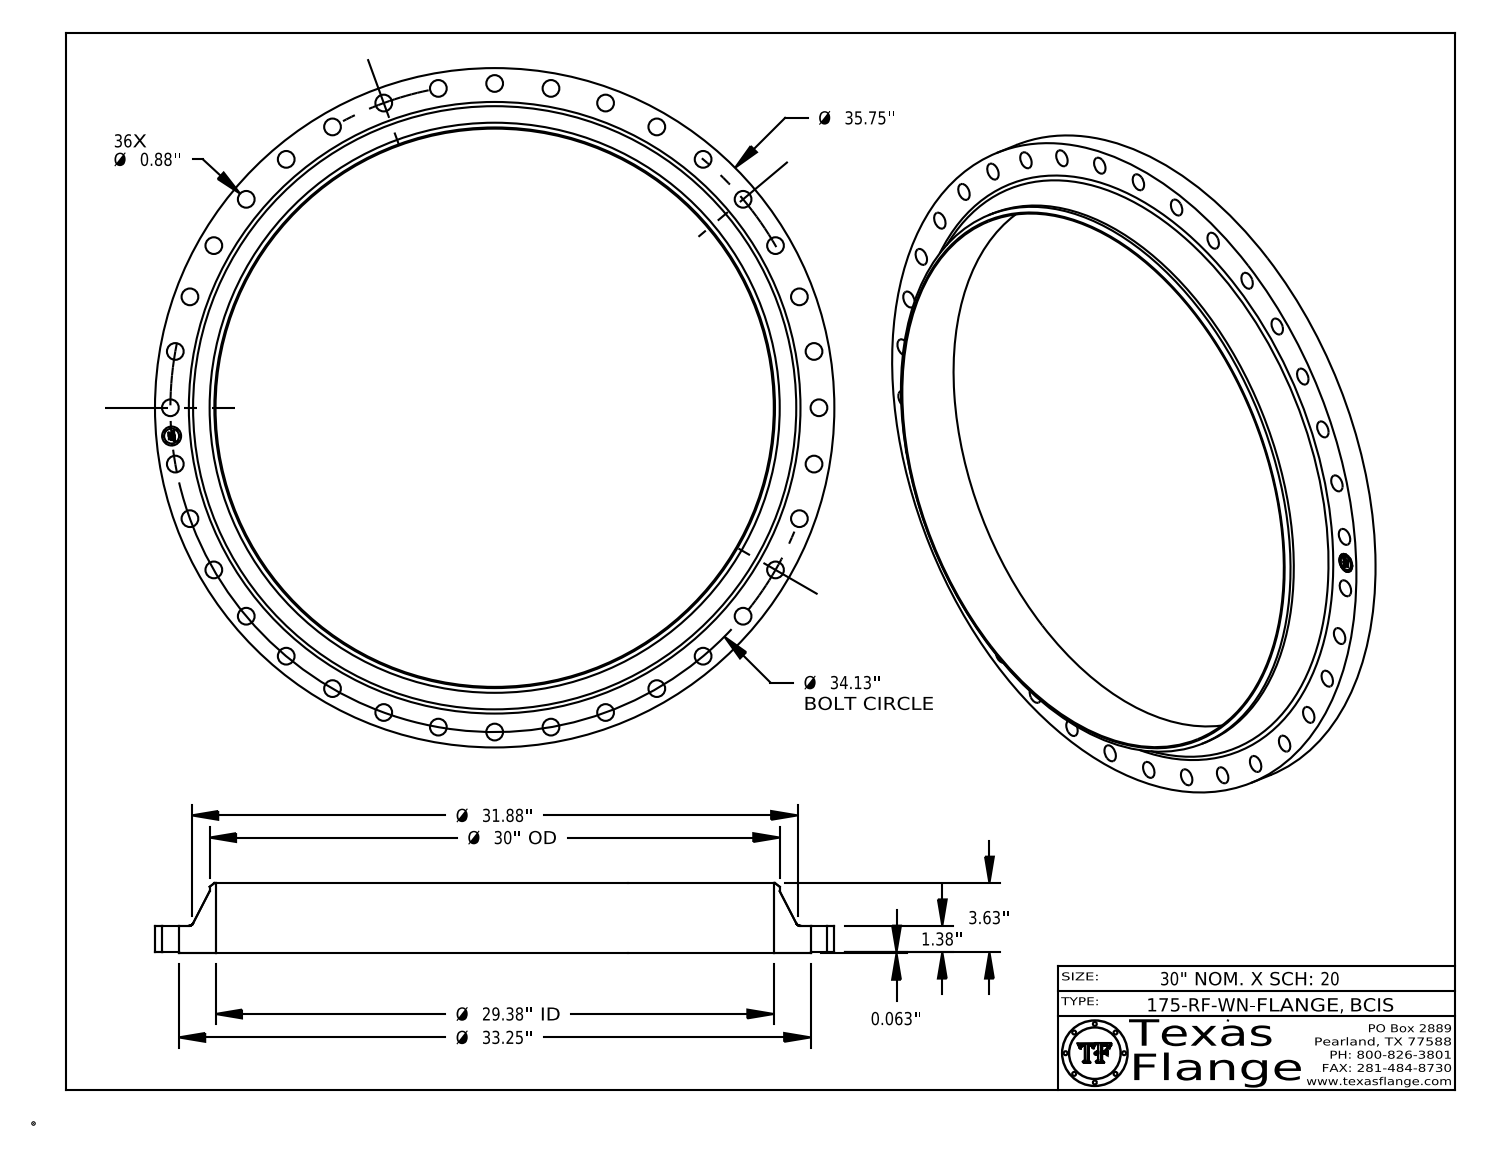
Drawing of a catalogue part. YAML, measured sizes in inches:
part_name: "175-RF-WN, BCIS"
step_written_by: "CATIA V5 STEP AP214 (AUTOMOTIVE_DESIGN)"
units: inches
bodies: {solids: 1, faces: 475, planar: 369, cylindrical: 100, other: 6}
overall_size: [35.75, 35.75, 3.693]
volume: 577.6
surface_area: 1381
round_holes:
  - {diameter: 0.88, count: 36}
  - {diameter: 1, count: 1}
  - {diameter: 29.376, count: 1}
round_bosses_or_shafts:
  - {diameter: 0.061, count: 8}
  - {diameter: 35.75, count: 1}
  - {diameter: 33.25, count: 1}
  - {diameter: 30, count: 1}
  - {diameter: 0.788, count: 1}
face_to_face_distances: [1.443, 0.063, 1.38, 3.693, 3.63, 2.25, 1.428, 1.365, 0.015, 2.265]
hole_center_spacings: [17.065, 29.557, 2.975, 5.927, 26.145, 34, 8.833, 21.939]
